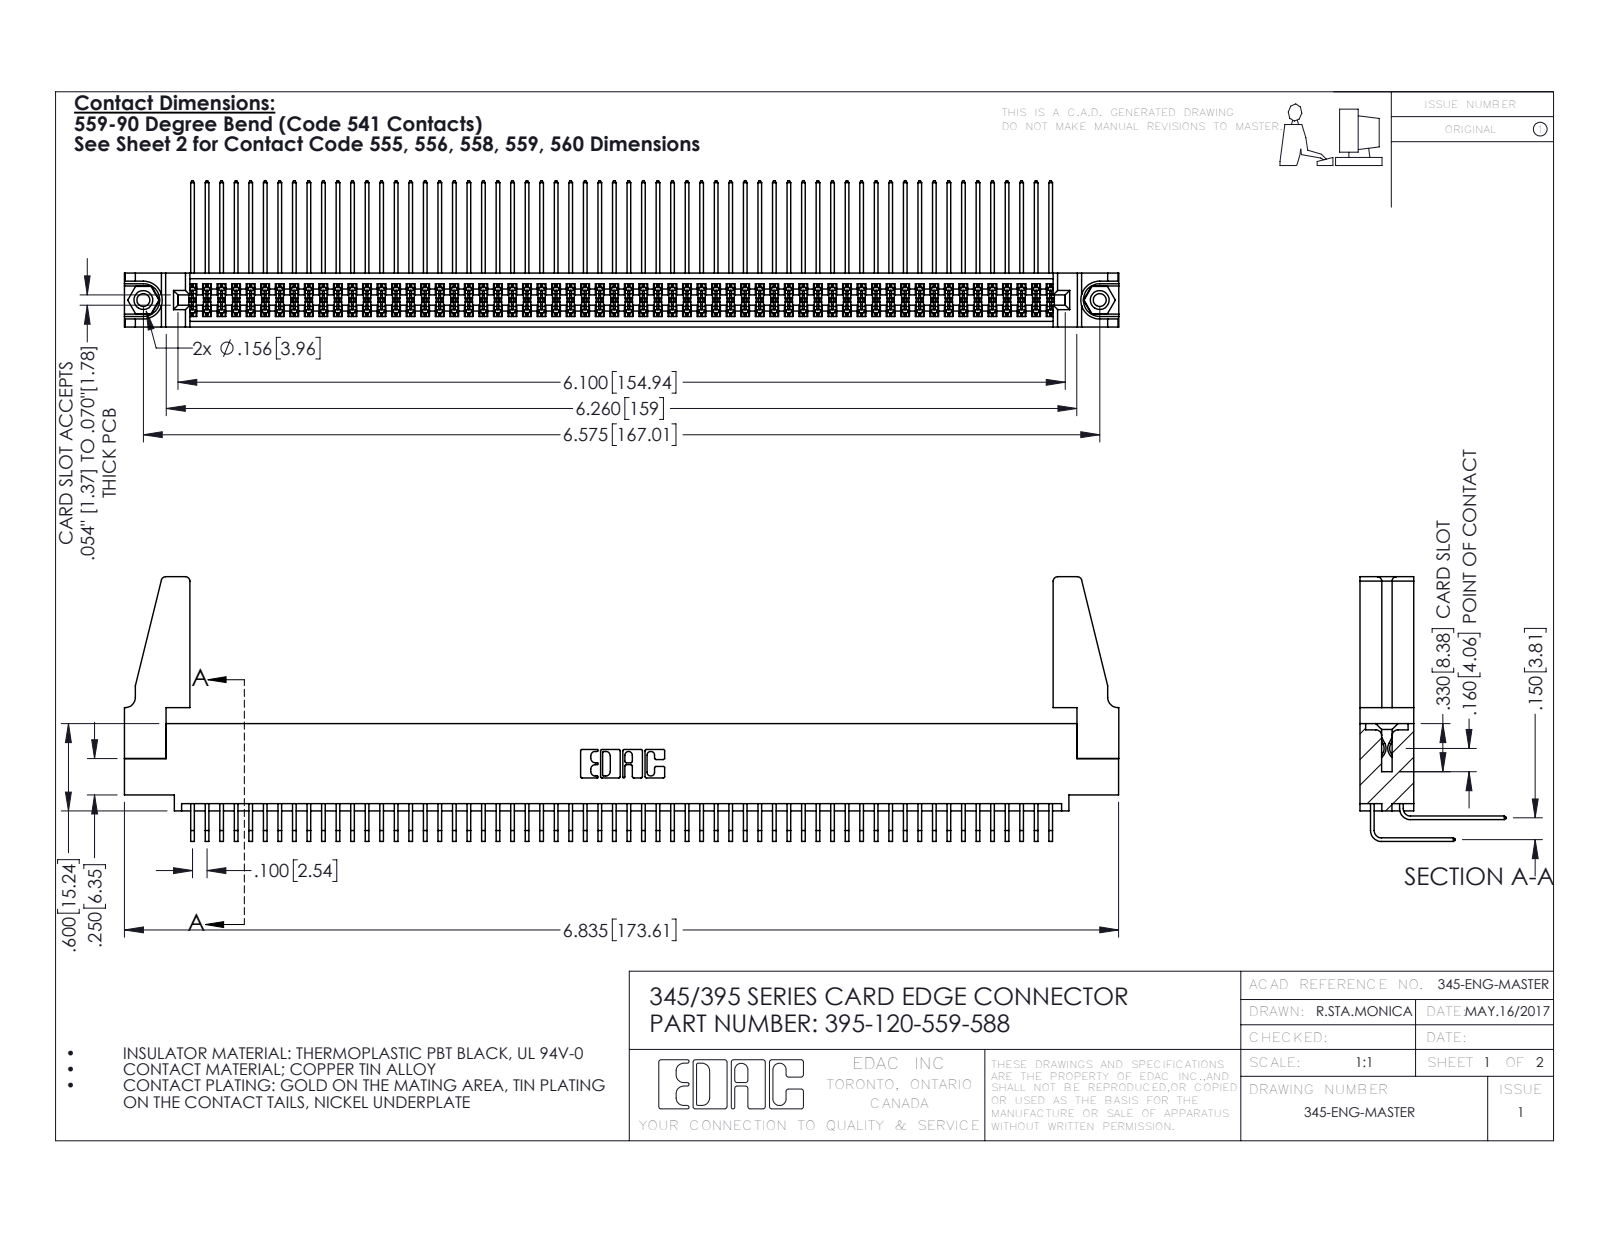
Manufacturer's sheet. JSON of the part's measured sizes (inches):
{"part_name": "345-292-001_558 559 Tail - 1; 345-220-078_345-220-088; 395-120-559-588; 345-292-001_559 Tail - 2 (+2 more)", "step_written_by": "SolidWorks 2016 (CONFIG_CONTROL_DESIGN)", "units": "inches", "bodies": {"solids": 125, "faces": 6494, "planar": 4356, "cylindrical": 2122, "other": 16}, "overall_size": [6.836, 1.819, 1.005], "volume_in3": 1.276, "surface_area_in2": 51.02, "round_holes": [[0.089, 2], [0.125, 2], [0.156, 2], [0.064, 1]], "round_bosses_or_shafts": [[0.155, 2]], "partial_cylinders_radius": [[0.006, 181], [0.01, 22], [0.03, 8], [0.007, 6], [0.031, 6], [0.026, 3], [0.014, 2], [0.019, 2]], "face_to_face_distances": [0.072, 0.298, 0.37, 0.2, 0.098, 0.272, 0.025, 0.225, 0.175, 0.15], "hole_center_spacings": [0.27, 6.339, 6.575]}
